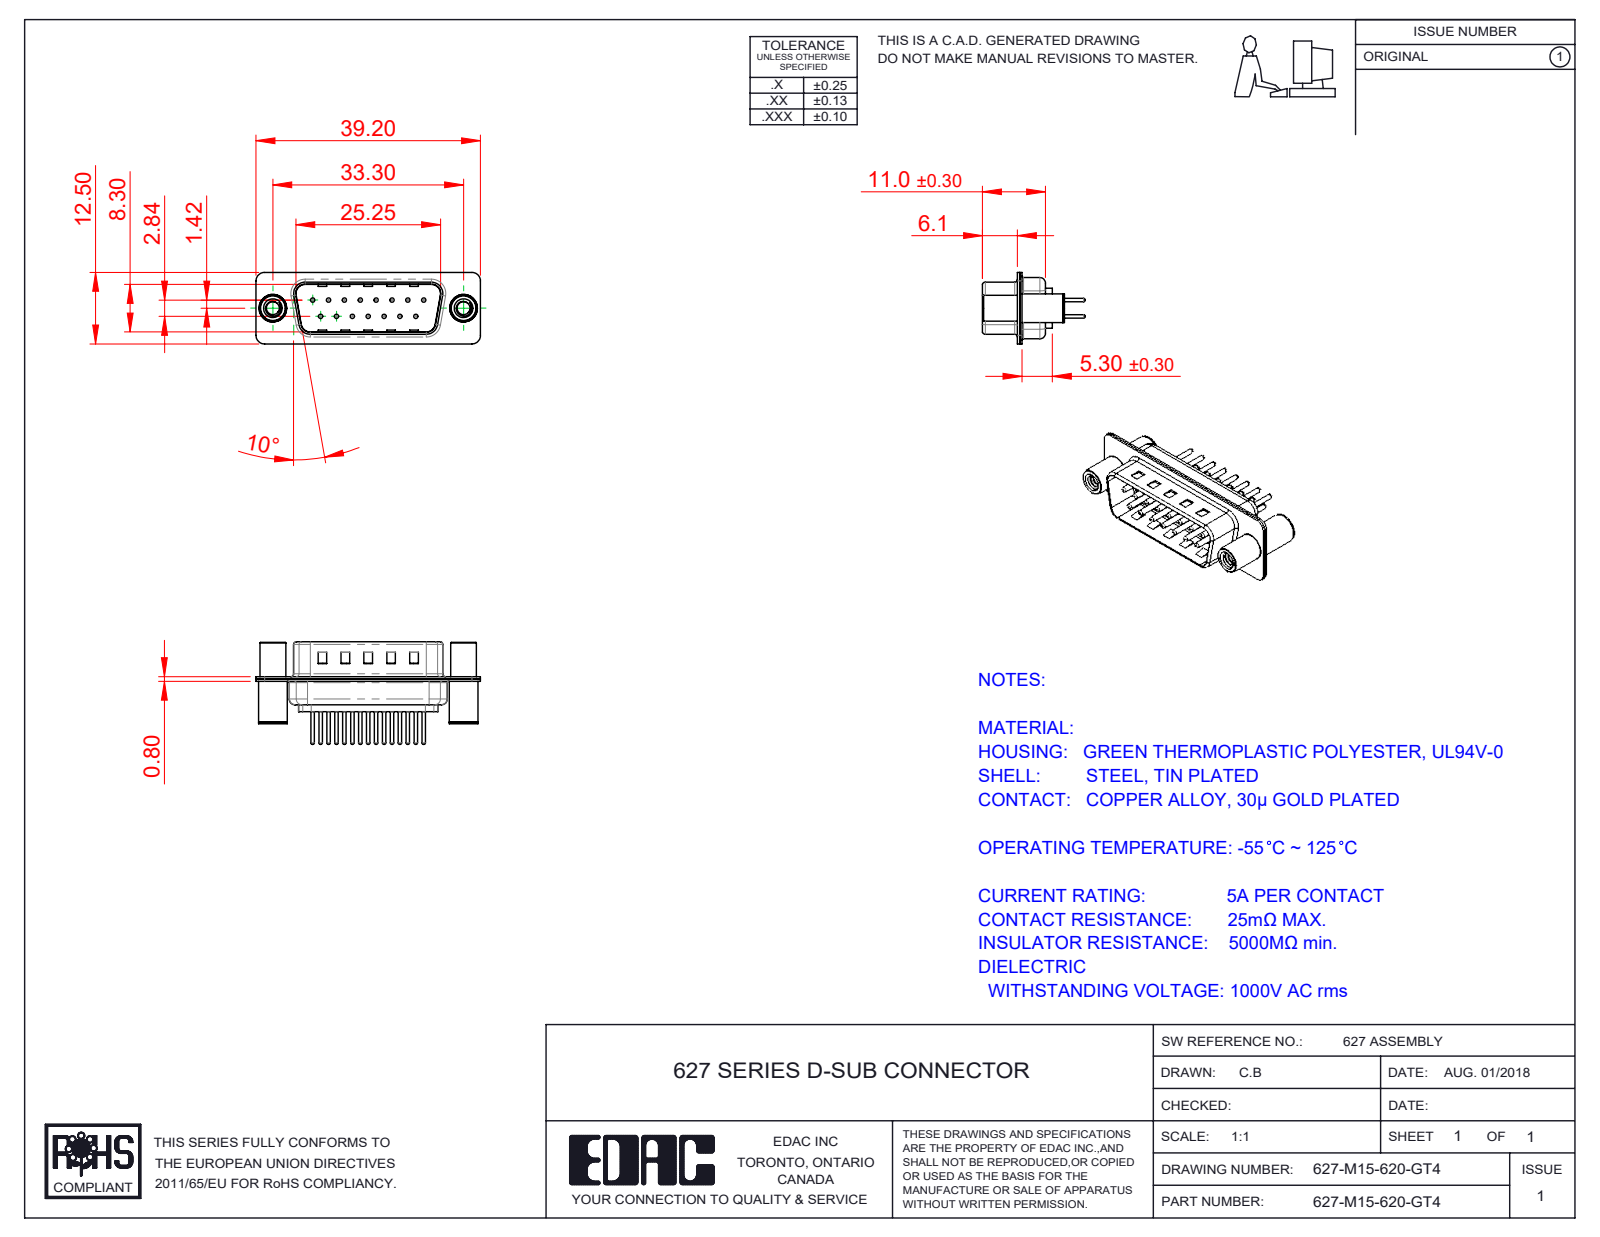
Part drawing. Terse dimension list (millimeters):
name: 627M Housing_15 Contacts; 627M Contact Row 1_20; 627M Shell Rear_15 Contacts; 627M Shell Front_15 Contacts (+3 more)
written by: SolidWorks 2020 (CONFIG_CONTROL_DESIGN)
unit: mm
bodies: 20 solids, 981 faces (250 planar, 395 cylindrical, 336 other)
size: 39.2 × 17.9 × 12.5
volume: 2 130 mm³; area: 5 337 mm²
holes: 15× ⌀0.75, 15× ⌀1.6, 15× ⌀2, 2× ⌀2.26, 2× ⌀3.26, 2× ⌀4, 2× ⌀4.8
bosses: 15× ⌀1.5, 15× ⌀0.6, 2× ⌀5, 2× ⌀4.9, 2× ⌀4.5
rounds: 16× R1.5, 12× R2, 8× R0.5, 8× R1.6, 4× R0.25, 4× R0.6, 4× R0.65, 4× R0.9
face distances: 0.4, 0.8, 9.5, 9.1, 8.7, 9.9, 1.2, 5.3, 6.1, 5.7
hole spacings: 3.16, 2.77, 5.54, 8.31, 11.08, 5.03, 5.04, 7.48
